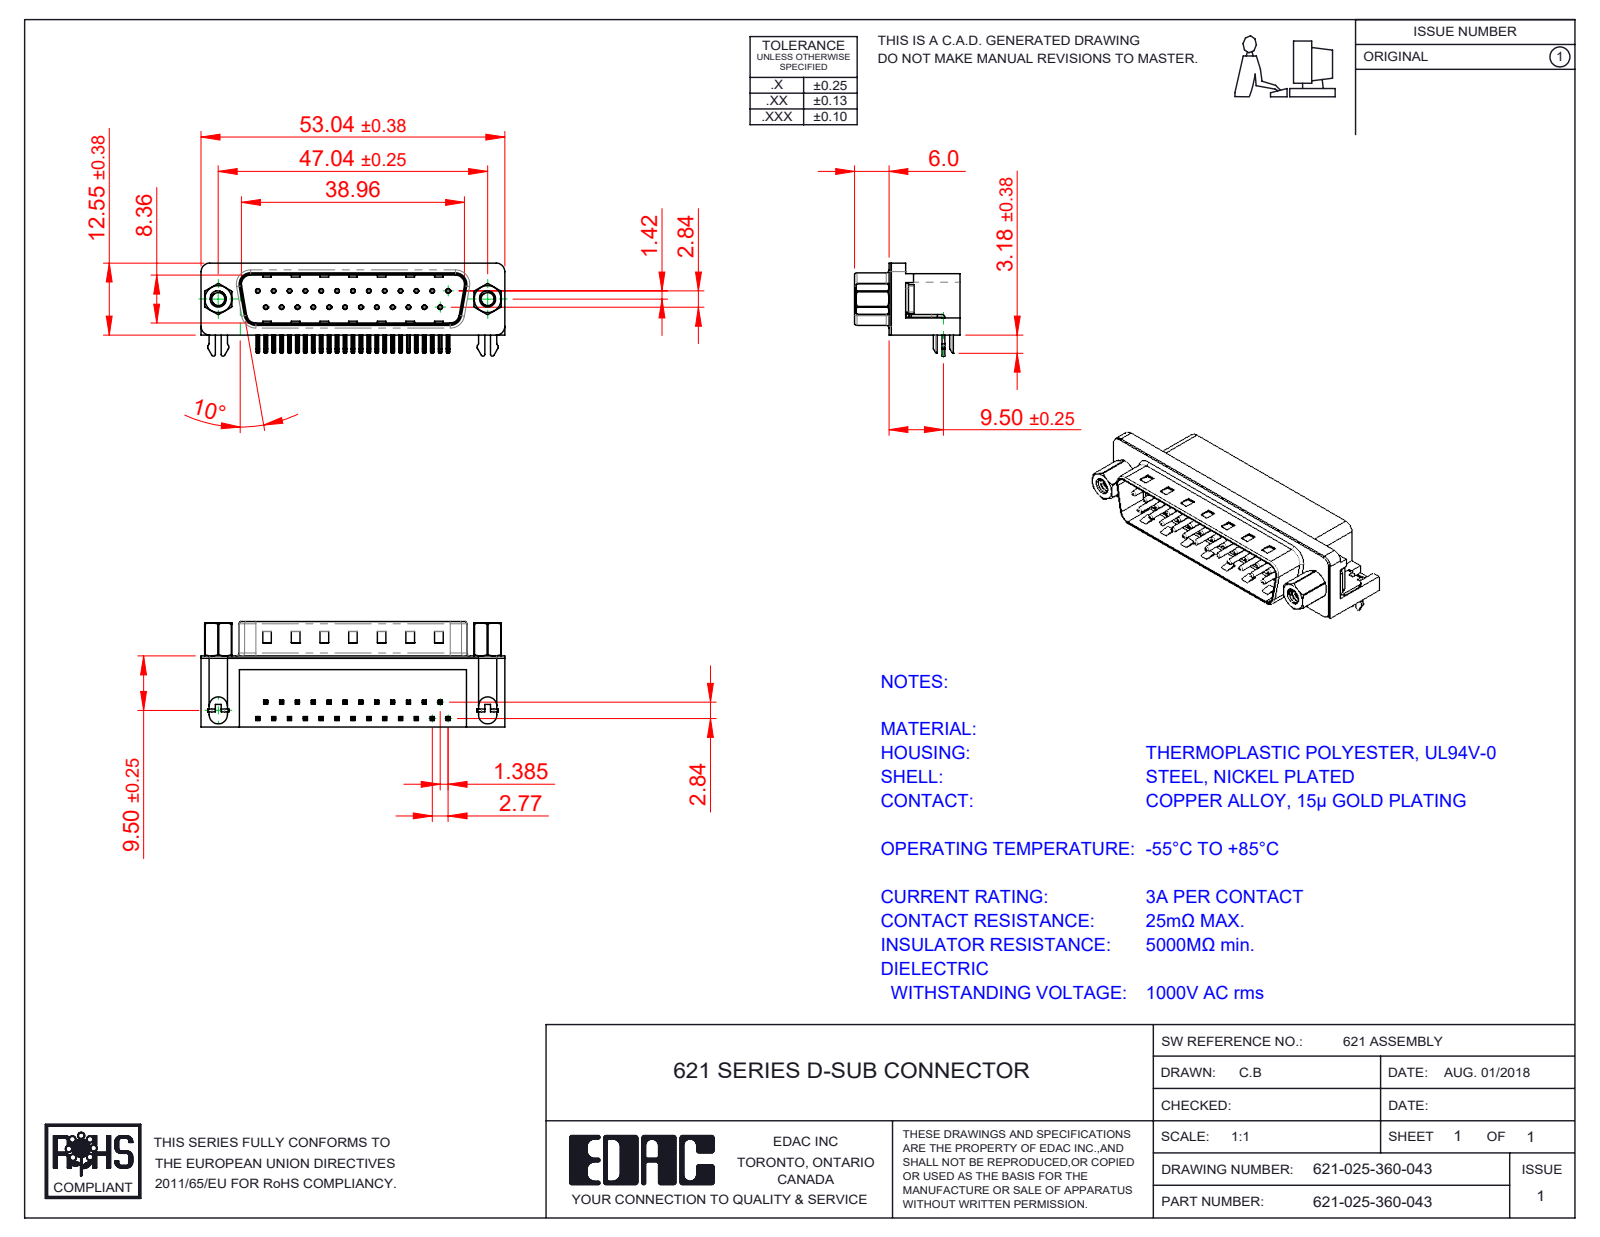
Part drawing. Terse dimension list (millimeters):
name: 621 4-40 Hex Standoff 5; 621 Housing_25 Socket; 621 Contact Bottom; 621-025-360-043 (+4 more)
written by: SolidWorks 2016 (CONFIG_CONTROL_DESIGN)
unit: mm
bodies: 33 solids, 2509 faces (1469 planar, 737 cylindrical, 303 other)
size: 53.04 × 18.4 × 16.25
volume: 6 570 mm³; area: 8 240 mm²
holes: 25× ⌀0.35, 25× ⌀0.8, 2× ⌀2, 2× ⌀2.26, 2× ⌀2.29, 2× ⌀4, 2× ⌀4.8, 2× ⌀5
bosses: 25× ⌀0.75, 2× ⌀4.9, 2× ⌀4.75, 2× ⌀3.9, 2× ⌀3, 2× ⌀2.79
rounds: 112× R0.25, 50× R0.12, 16× R1, 9× R0.5, 8× R1.6, 7× R1.5, 4× R0.9, 4× R2
face distances: 0.4, 12, 10.35, 2.1, 8.76, 10.46, 1.7, 10.86, 12.4, 9
hole spacings: 3.16, 2.77, 5.54, 8.31, 11.08, 13.85, 16.62, 5.03
